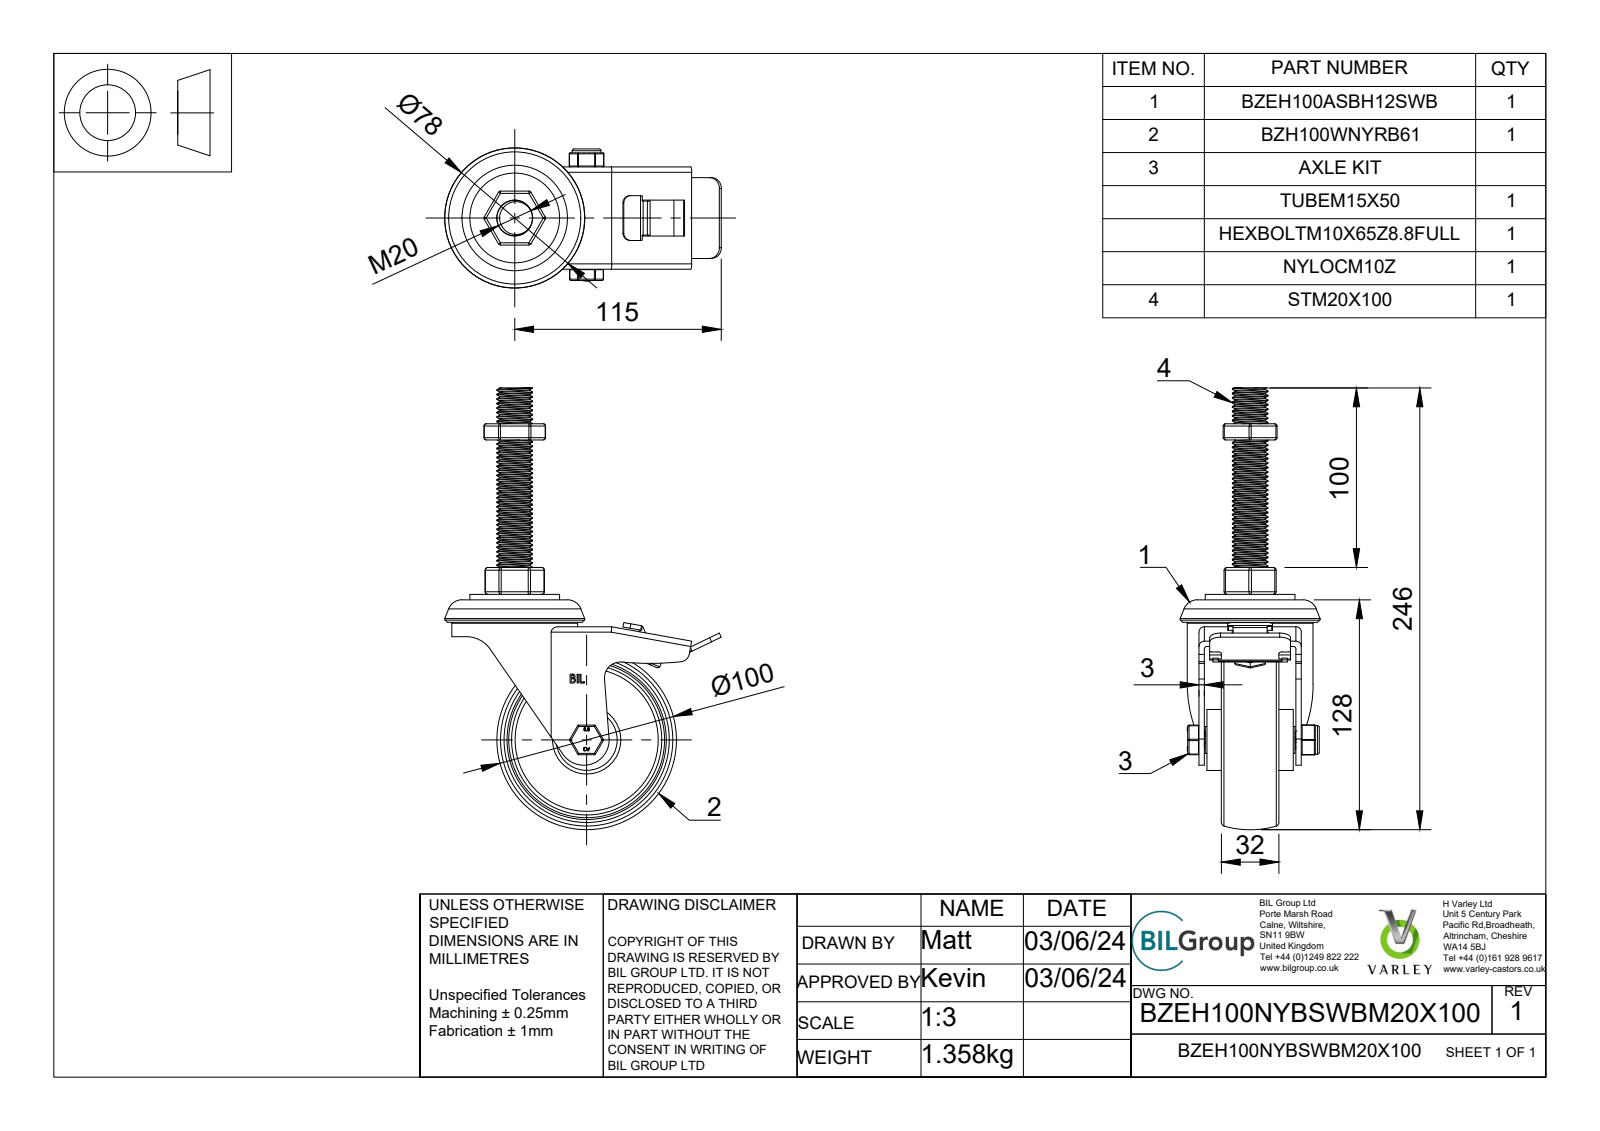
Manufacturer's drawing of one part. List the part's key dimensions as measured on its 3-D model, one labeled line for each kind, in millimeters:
Part name (STEP PRODUCT): BZEH100NYBSWBM20X100 v3; BZEH100ASBH12SWB v1; ZINC PLATED, PRESSED STEEL TOP HEAD; ZINC PLATED, PRESSED STEEL FORKS (+8 more)
STEP written by: Autodesk Translation Framework v13.14.0.145 (AUTOMOTIVE_DESIGN)
Units: millimetres
Bodies: 26 solids, 915 faces (370 planar, 410 cylindrical, 135 other)
Overall size (bounding box): 246 × 154 × 78
Volume: 277 052 mm³ · Surface area: 146 695 mm²
Round holes (diameter × count): ⌀12 ×2, ⌀15 ×2, ⌀8 ×1, ⌀10 ×1, ⌀10.2 ×1, ⌀10.5 ×1, ⌀12.2 ×1, ⌀15.2 ×1, ⌀20 ×1, ⌀30 ×1, ⌀64 ×1
Round bosses / shafts (diameter × count): ⌀4 ×8, ⌀70 ×1, ⌀53.5 ×1, ⌀50 ×1, ⌀34 ×1, ⌀28.75 ×1, ⌀25 ×1, ⌀23.5 ×1
Partial cylindrical surfaces — rounded edges, fillets, slot ends (radius × count): R0.5 ×32, R1.5 ×24, R1.25 ×18, R0.75 ×12, R1 ×8, R3 ×4, R2 ×3, R4 ×3
Main face-to-face distances: 3, 8, 29.5, 32.5, 24.5, 21.5, 54, 5, 13, 2.5
